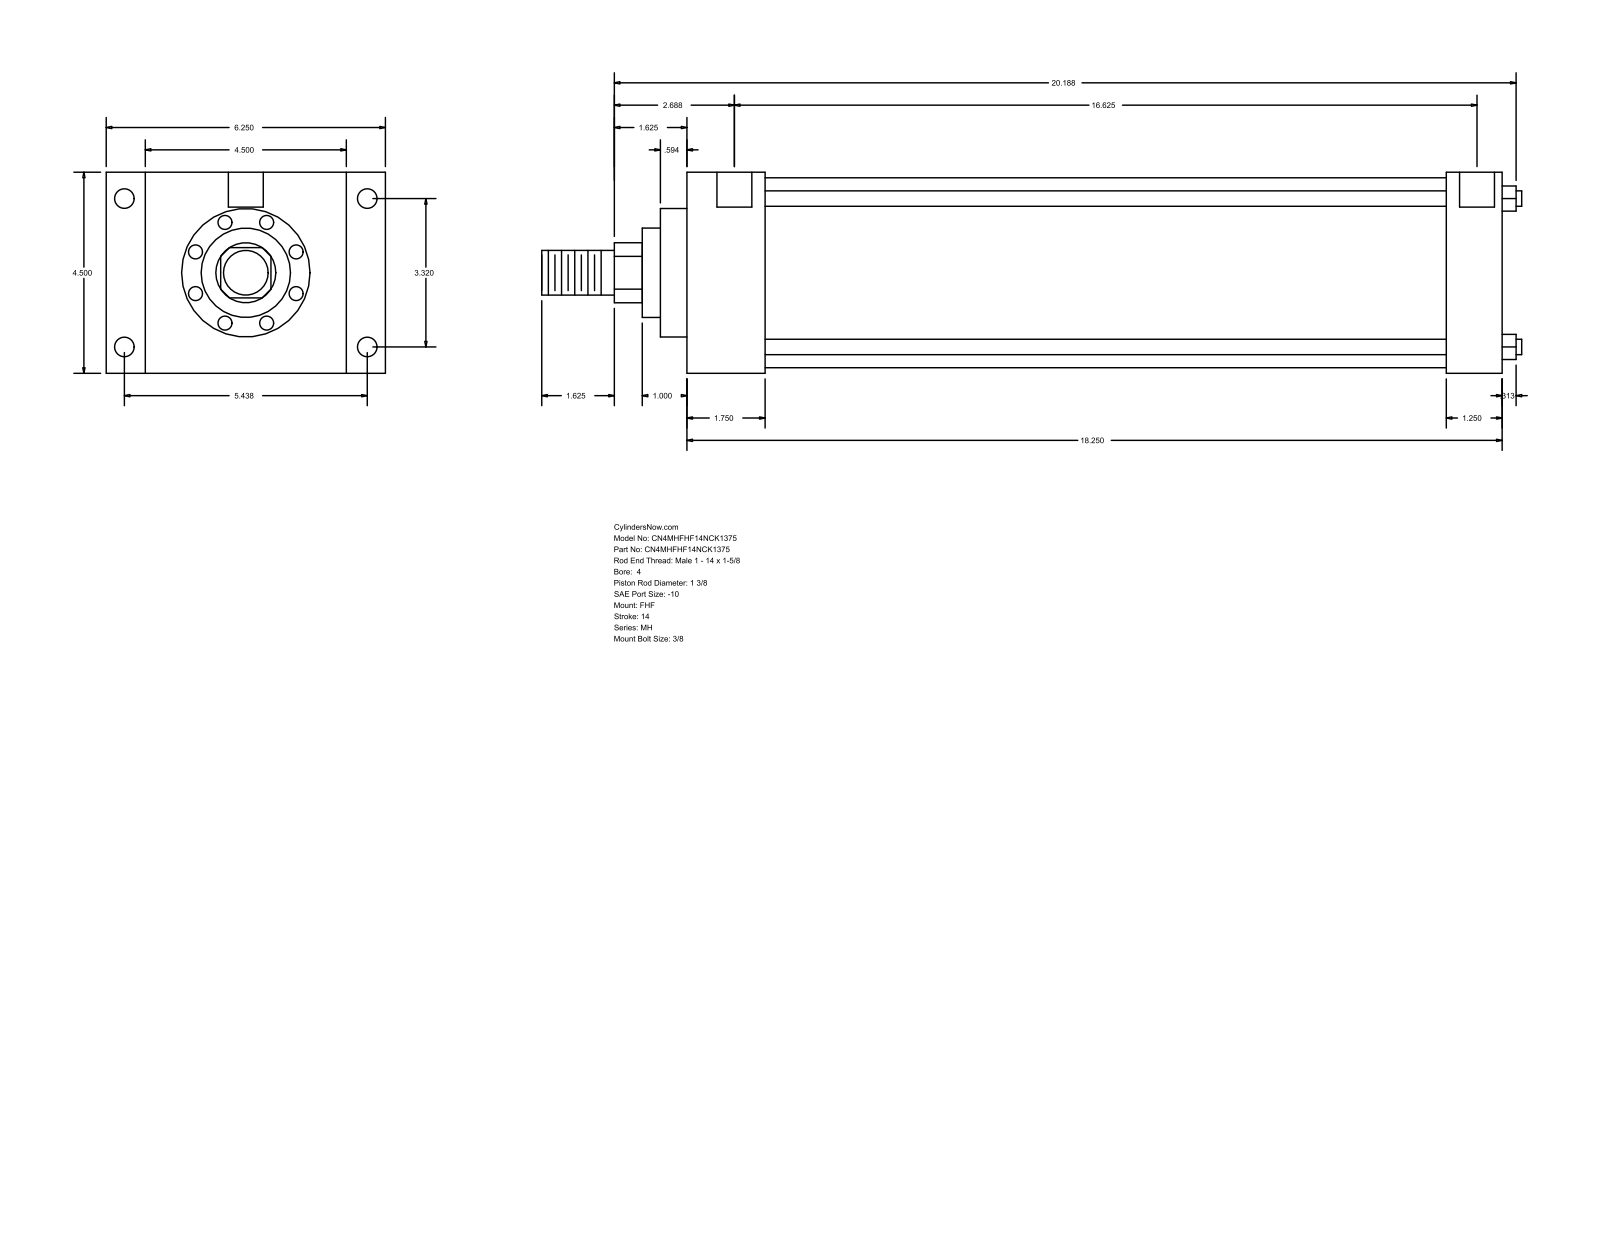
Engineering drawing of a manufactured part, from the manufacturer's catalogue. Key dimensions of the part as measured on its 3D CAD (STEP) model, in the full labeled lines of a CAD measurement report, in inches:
Part name (STEP PRODUCT): MH_FHF__0400_1.375
STEP written by: GSSL Pune (CONFIG_CONTROL_DESIGN)
Units: inches
Bodies: 0 solids, 90 faces (61 planar, 29 cylindrical, 0 other)
Overall size (bounding box): 21.937 × 6.25 × 4.5
Round holes (diameter × count): ⌀0.344 ×4, ⌀0.438 ×4, ⌀0.781 ×2
Round bosses / shafts (diameter × count): ⌀0.345 ×4, ⌀4.25 ×1, ⌀2.875 ×1, ⌀2 ×1, ⌀1.375 ×1, ⌀1 ×1
Partial cylindrical surfaces — rounded edges, fillets, slot ends (radius × count): R0.672 ×1
Main face-to-face distances: 4.5, 18.25, 1.75, 16.5, 0.875, 5.375, 6.25, 17, 15.25, 1.25
Hole centre spacings: 3.32, 5.438, 6.371, 16.75, 0.062, 0.063, 16.625, 16.687
